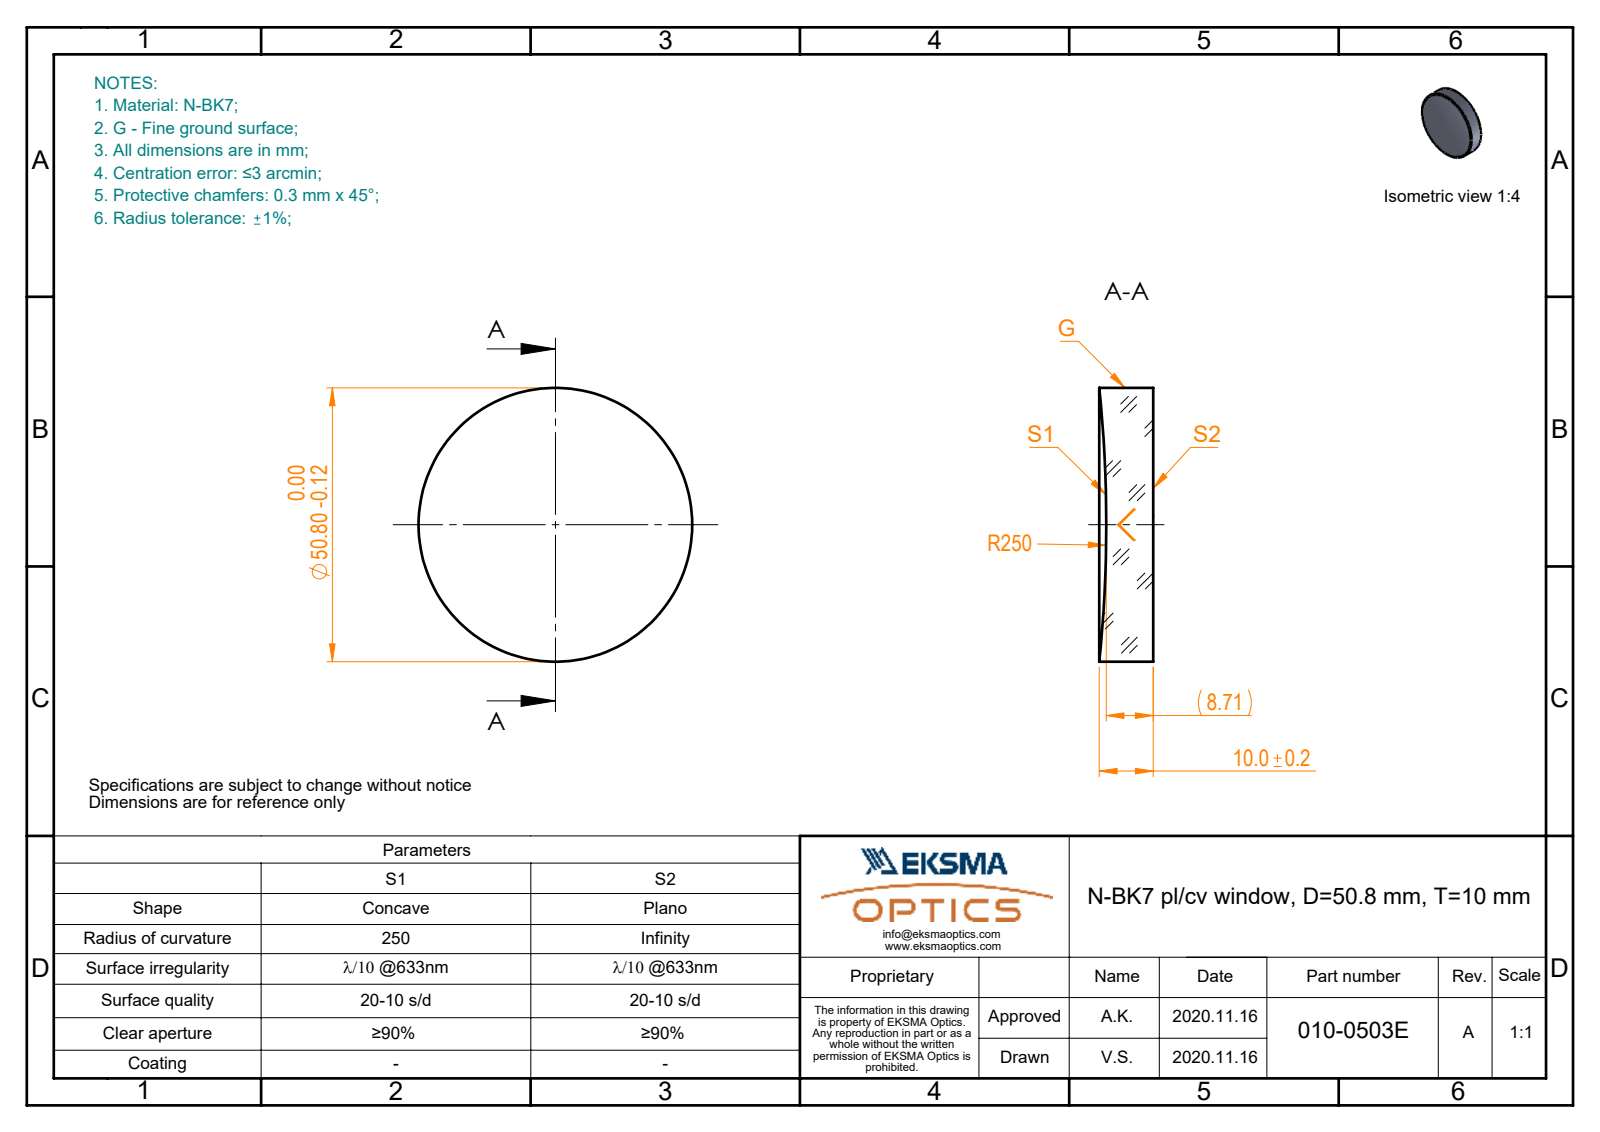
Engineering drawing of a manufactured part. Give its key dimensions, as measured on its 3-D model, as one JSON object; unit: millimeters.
{"part_name": "010-0503E_N-BK7_PCV_window", "step_written_by": "SolidWorks 2019 (CONFIG_CONTROL_DESIGN)", "units": "millimeters", "bodies": {"solids": 1, "faces": 5, "planar": 1, "cylindrical": 2, "other": 2}, "overall_size": [50.8, 50.8, 10], "volume_mm3": 18956, "surface_area_mm2": 5655, "round_bosses_or_shafts": [[50.8, 1]]}
